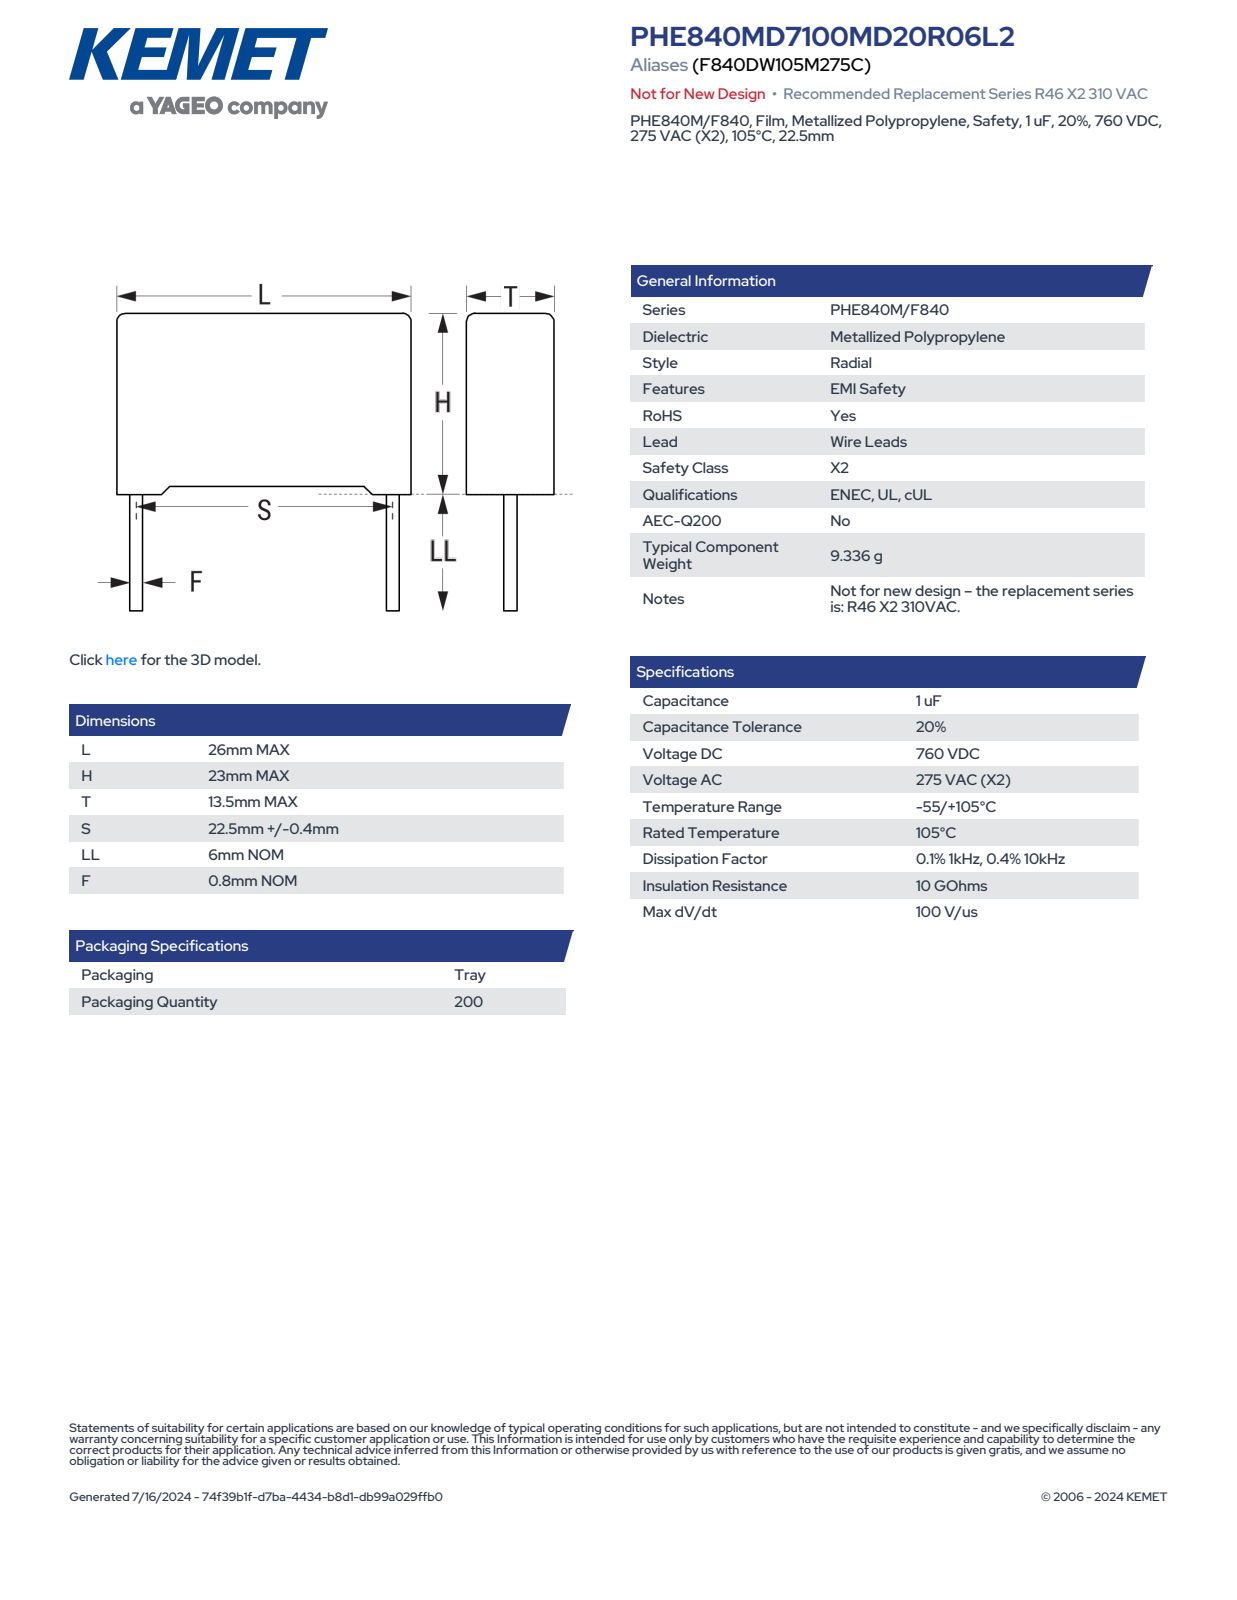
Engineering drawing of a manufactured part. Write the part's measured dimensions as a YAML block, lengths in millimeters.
part_name: "CFR_RB2_26X23X13.5_L26H23T13.5S22.5LL6F0.8"
step_written_by: "SolidWorks 2021 (AUTOMOTIVE_DESIGN)"
units: millimeters
bodies: {solids: 4, faces: 85, planar: 77, cylindrical: 8, other: 0}
overall_size: [29, 26, 13.51]
volume: 7827
surface_area: 2584
round_bosses_or_shafts:
  - {diameter: 0.8, count: 2}
partial_cylinders:
  - {radius: 0.5, count: 4}
face_to_face_distances: [13.5, 26, 22.21, 22.25, 0.79, 0.75, 23, 0.87, 25.13, 24.26]
